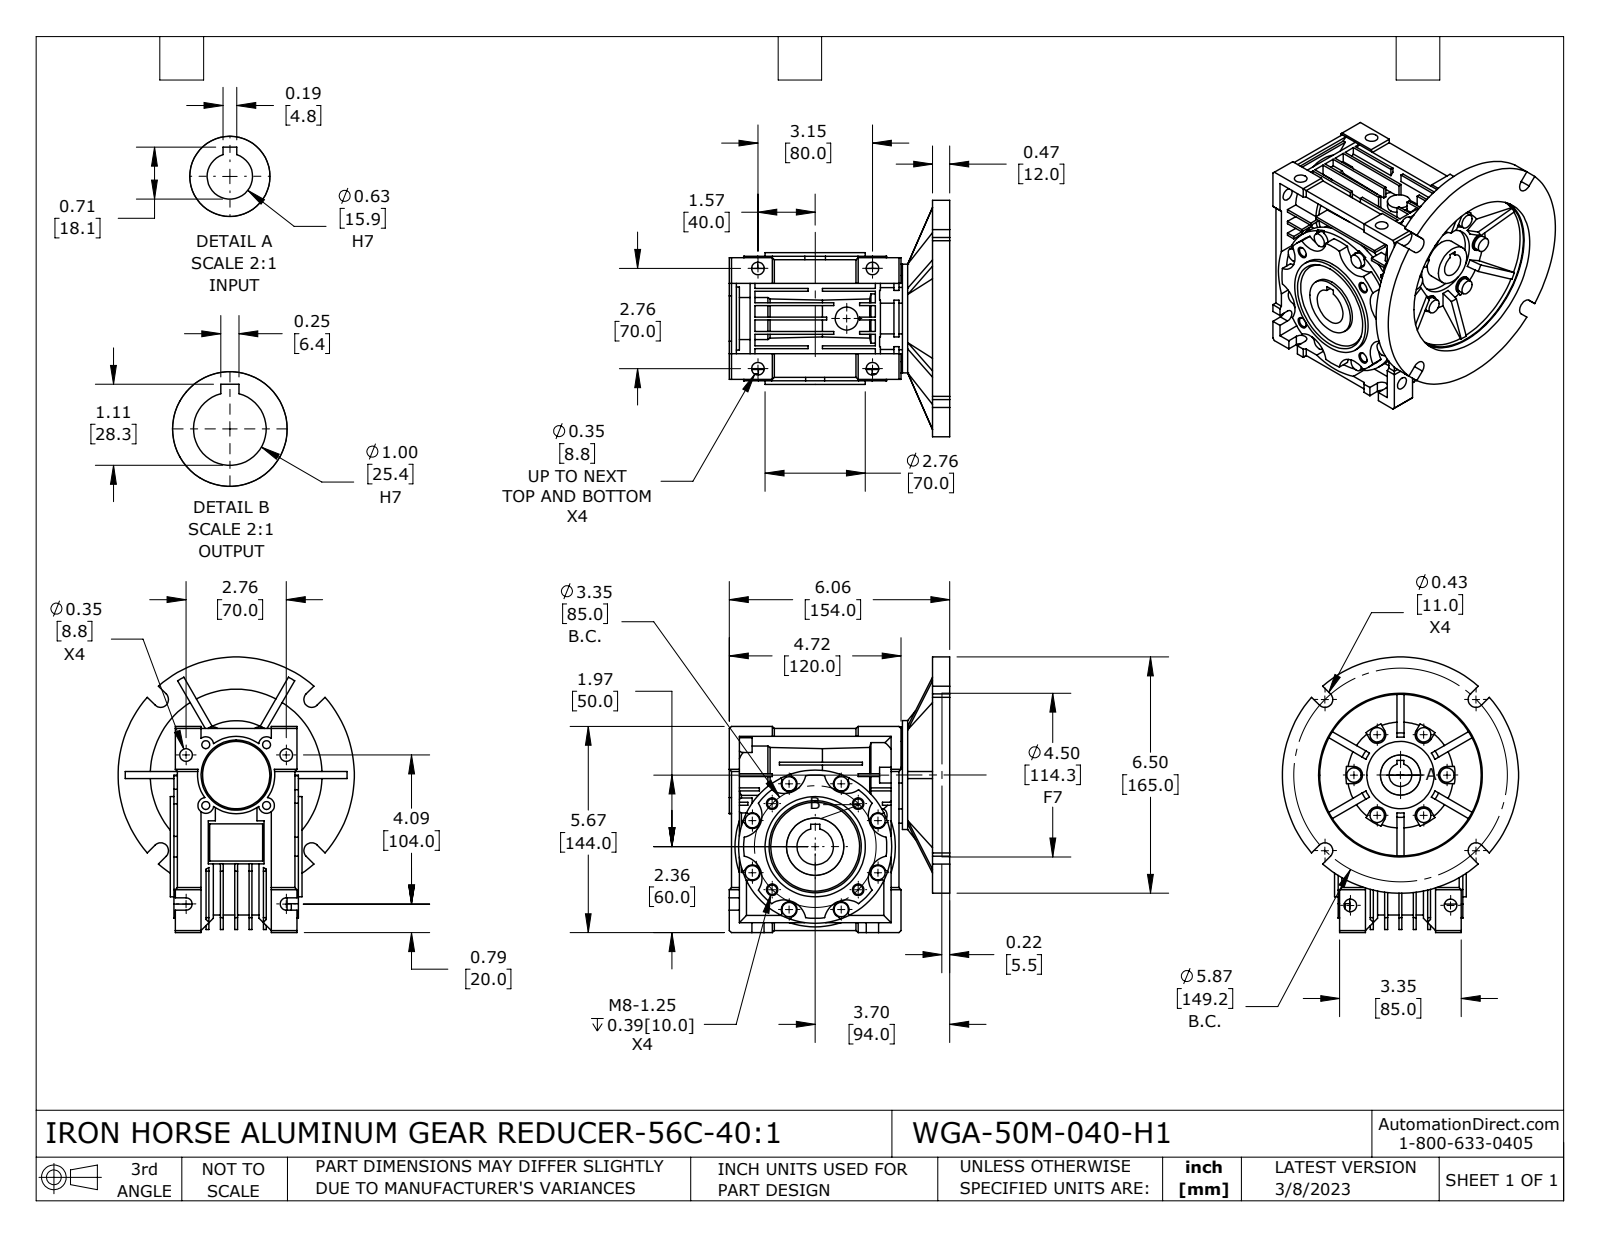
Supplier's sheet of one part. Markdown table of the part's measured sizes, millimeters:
| quantity | value |
| --- | --- |
| part name | WGA-50M-040-H1 |
| STEP written by | SolidWorks 2021 (CONFIG_CONTROL_DESIGN) |
| units | millimeters |
| bodies | 4 solids, 954 faces (558 planar, 292 cylindrical, 104 other) |
| overall size | 192.5 × 165 × 154 |
| volume | 1 191 000 mm³ |
| surface area | 266 100 mm² |
| round holes (diameter × count) | 8.8 × 8, 5.6 × 4, 6.7 × 4, 6.7 × 2, 15.9 × 1, 16.5 × 1, 25.4 × 1, 28 × 1, 34 × 1, 40 × 1, 47 × 1, 112.8 × 1 |
| round bosses / shafts (diameter × count) | 10 × 14, 165 × 1, 107 × 1, 76 × 1, 70 × 1, 61 × 1, 55 × 1, 54 × 1 |
| partial cylindrical surfaces (radius × count) | 5.5 × 22, 6 × 14, 15 × 8, 15.5 × 8, 4.2 × 6, 46 × 1, 47.7 × 1, 50 × 1 |
| main face-to-face distances | 12, 10, 2, 7, 8, 1.5, 5.5, 20, 55, 35 |
| hole center spacings | 30, 42.4, 42.5, 60.1, 70, 15.6, 37.7, 37.8 |
